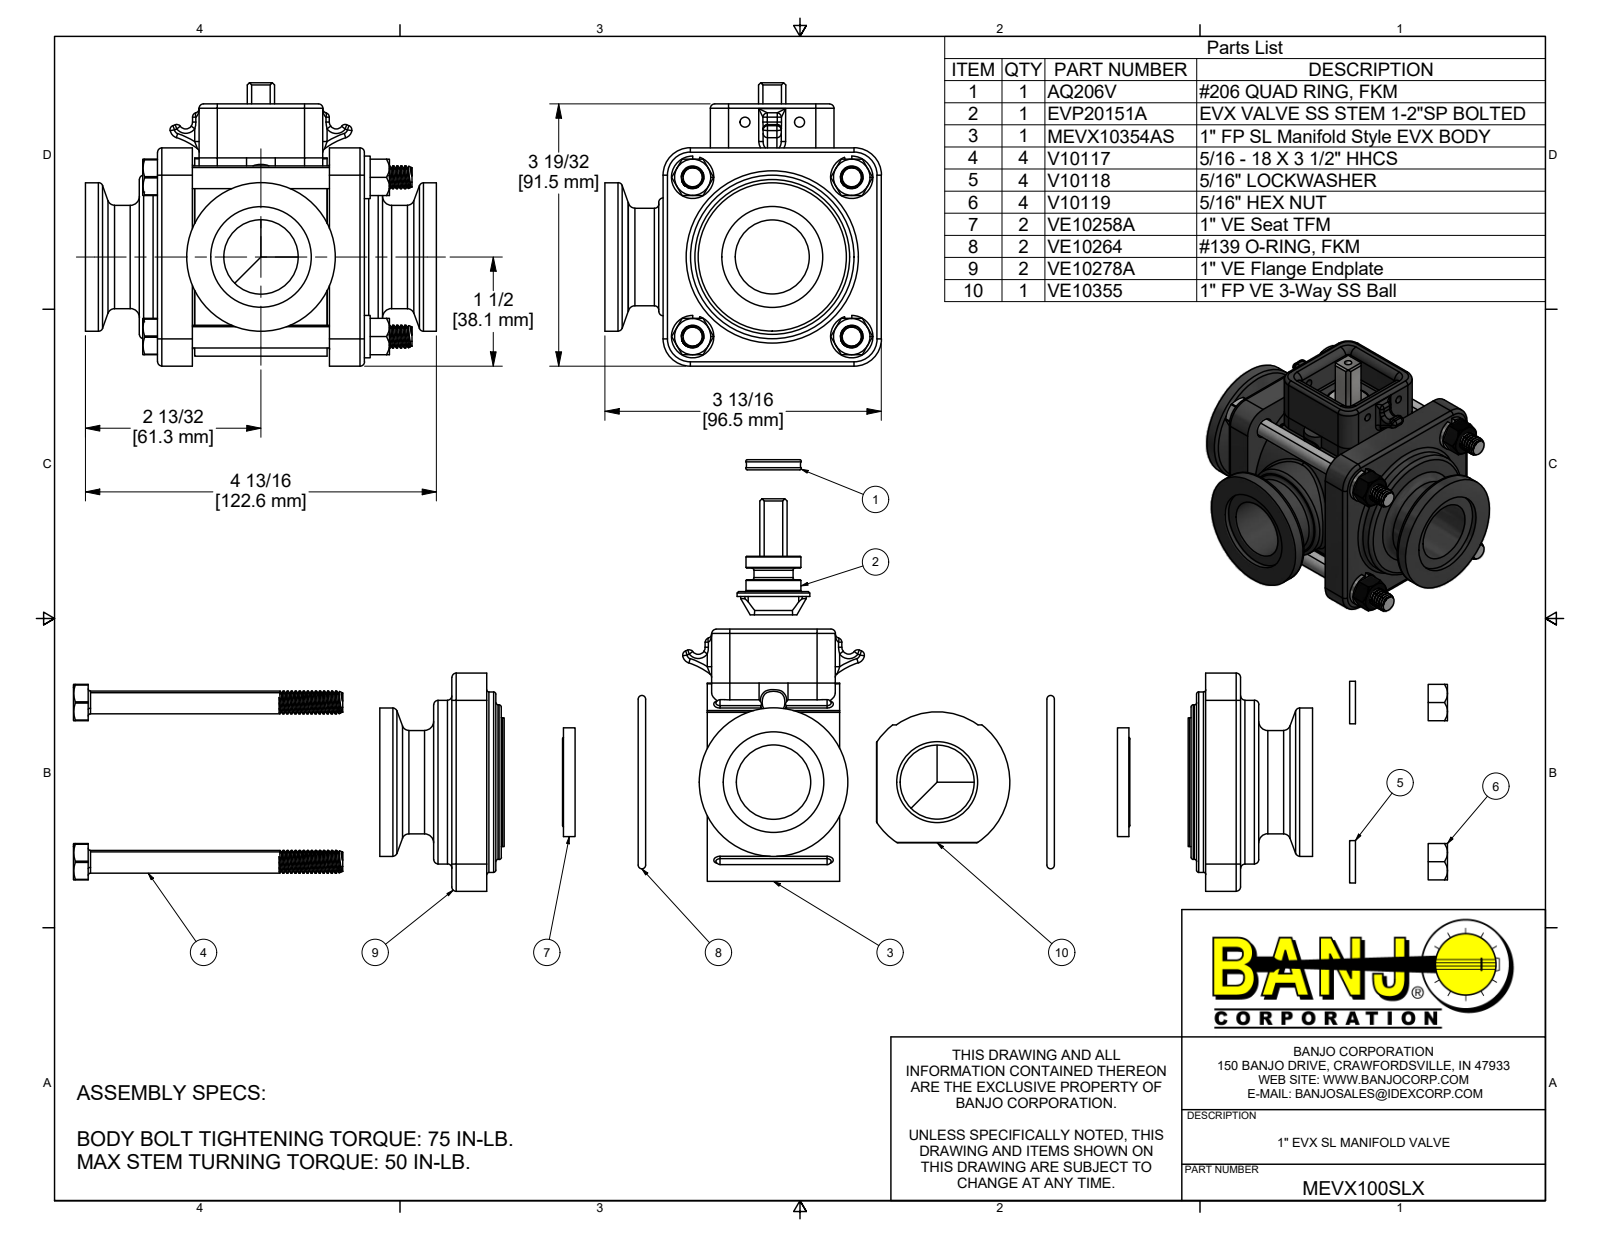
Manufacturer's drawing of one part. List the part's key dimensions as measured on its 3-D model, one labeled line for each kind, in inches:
Part name (STEP PRODUCT): MEVX100SLX; MEVX10354AS; MEVX10354ASX; VE10355 (+8 more)
STEP written by: Autodesk Inventor 2019 (AUTOMOTIVE_DESIGN)
Units: inches
Bodies: 22 solids, 1325 faces (222 planar, 526 cylindrical, 577 other)
Overall size (bounding box): 4.825 × 3.893 × 3.8
Volume: 22.3 in³ · Surface area: 192.8 in²
Round holes (diameter × count): ⌀0.252 ×4, ⌀0.322 ×4, ⌀0.35 ×4, ⌀1.02 ×3, ⌀0.135 ×2, ⌀0.76 ×1, ⌀1.38 ×1, ⌀1.39 ×1, ⌀1.5 ×1, ⌀2.12 ×1, ⌀2.375 ×1, ⌀2.5 ×1
Round bosses / shafts (diameter × count): ⌀0.268 ×60, ⌀0.583 ×4, ⌀0.313 ×4, ⌀2.04 ×2, ⌀2.725 ×1, ⌀2.48 ×1, ⌀2.25 ×1, ⌀2.124 ×1
Partial cylindrical surfaces — rounded edges, fillets, slot ends (radius × count): R0.06 ×42, R0.03 ×12, R0.062 ×8, R0.134 ×8, R0.375 ×8, R0.125 ×6, R0.21 ×4, R0.25 ×4
Main face-to-face distances: 0.48, 2.365, 2.845, 3, 0.99, 1.47, 3.355, 3.835, 1.885, 0.605
Hole centre spacings: 1.547, 2.188, 1.891, 3.094, 3.294, 0.75, 1.046, 1.046
